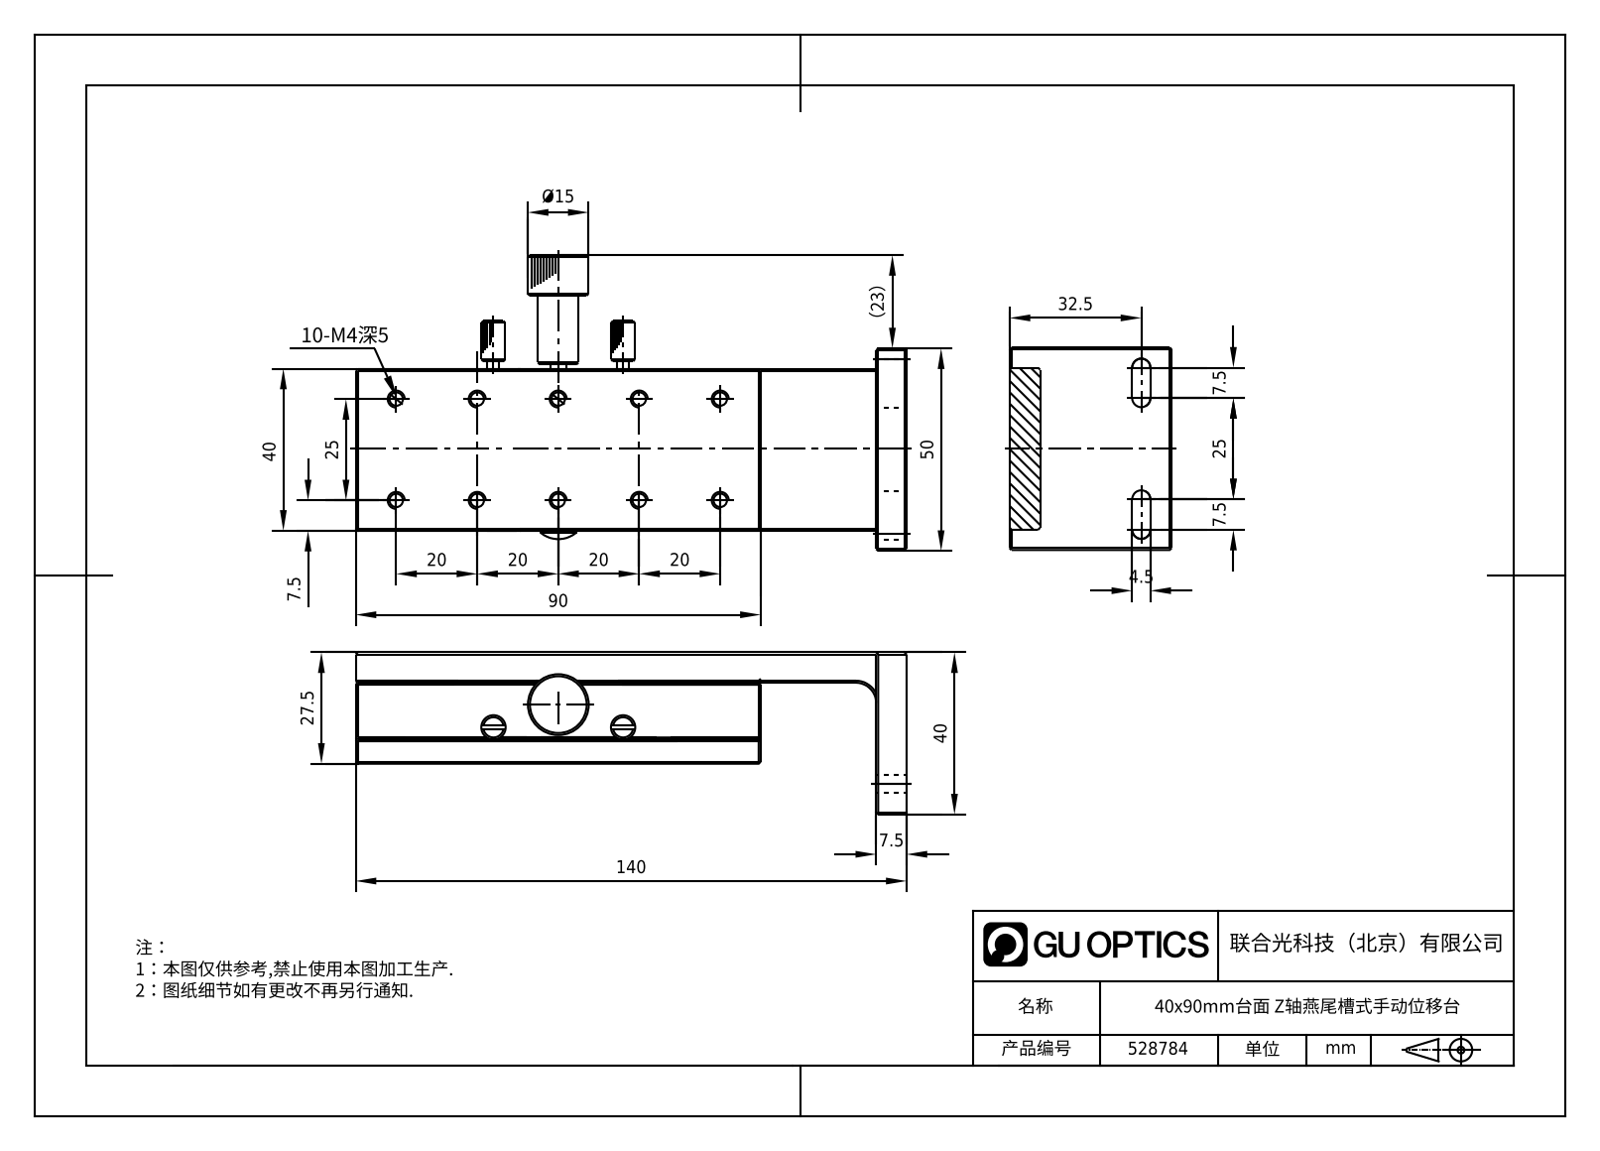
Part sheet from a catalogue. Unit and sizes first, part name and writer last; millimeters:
Units: millimetres
Overall size (bounding box): 140 × 77.9 × 40
Round holes (diameter × count): ⌀2.5 ×15, ⌀3.3 ×14, ⌀4.5 ×7, ⌀8 ×7, ⌀2.05 ×3, ⌀3.4 ×3, ⌀6 ×3, ⌀2.8 ×2, ⌀2.9 ×1, ⌀4 ×1, ⌀4.1 ×1, ⌀5 ×1
Round bosses / shafts (diameter × count): ⌀7 ×6, ⌀4 ×4, ⌀3 ×4, ⌀5.5 ×3, ⌀10 ×2, ⌀9 ×2, ⌀2.95 ×2, ⌀8 ×1
Partial cylindrical surfaces — rounded edges, fillets, slot ends (radius × count): R2.25 ×4, R2 ×2, R10 ×1
Main face-to-face distances: 7.5, 20, 6, 14, 27.5, 21.5, 40, 10, 3.8, 4
Hole centre spacings: 15.21, 20, 31.32, 32.02, 25, 30, 40, 47.17
Volume: 126 346 mm³ · Surface area: 55 948 mm²
Bodies: 20 solids, 956 faces (569 planar, 199 cylindrical, 188 other)
Part name (STEP PRODUCT): 528784
STEP written by: SolidWorks 2020 (CONFIG_CONTROL_DESIGN)
